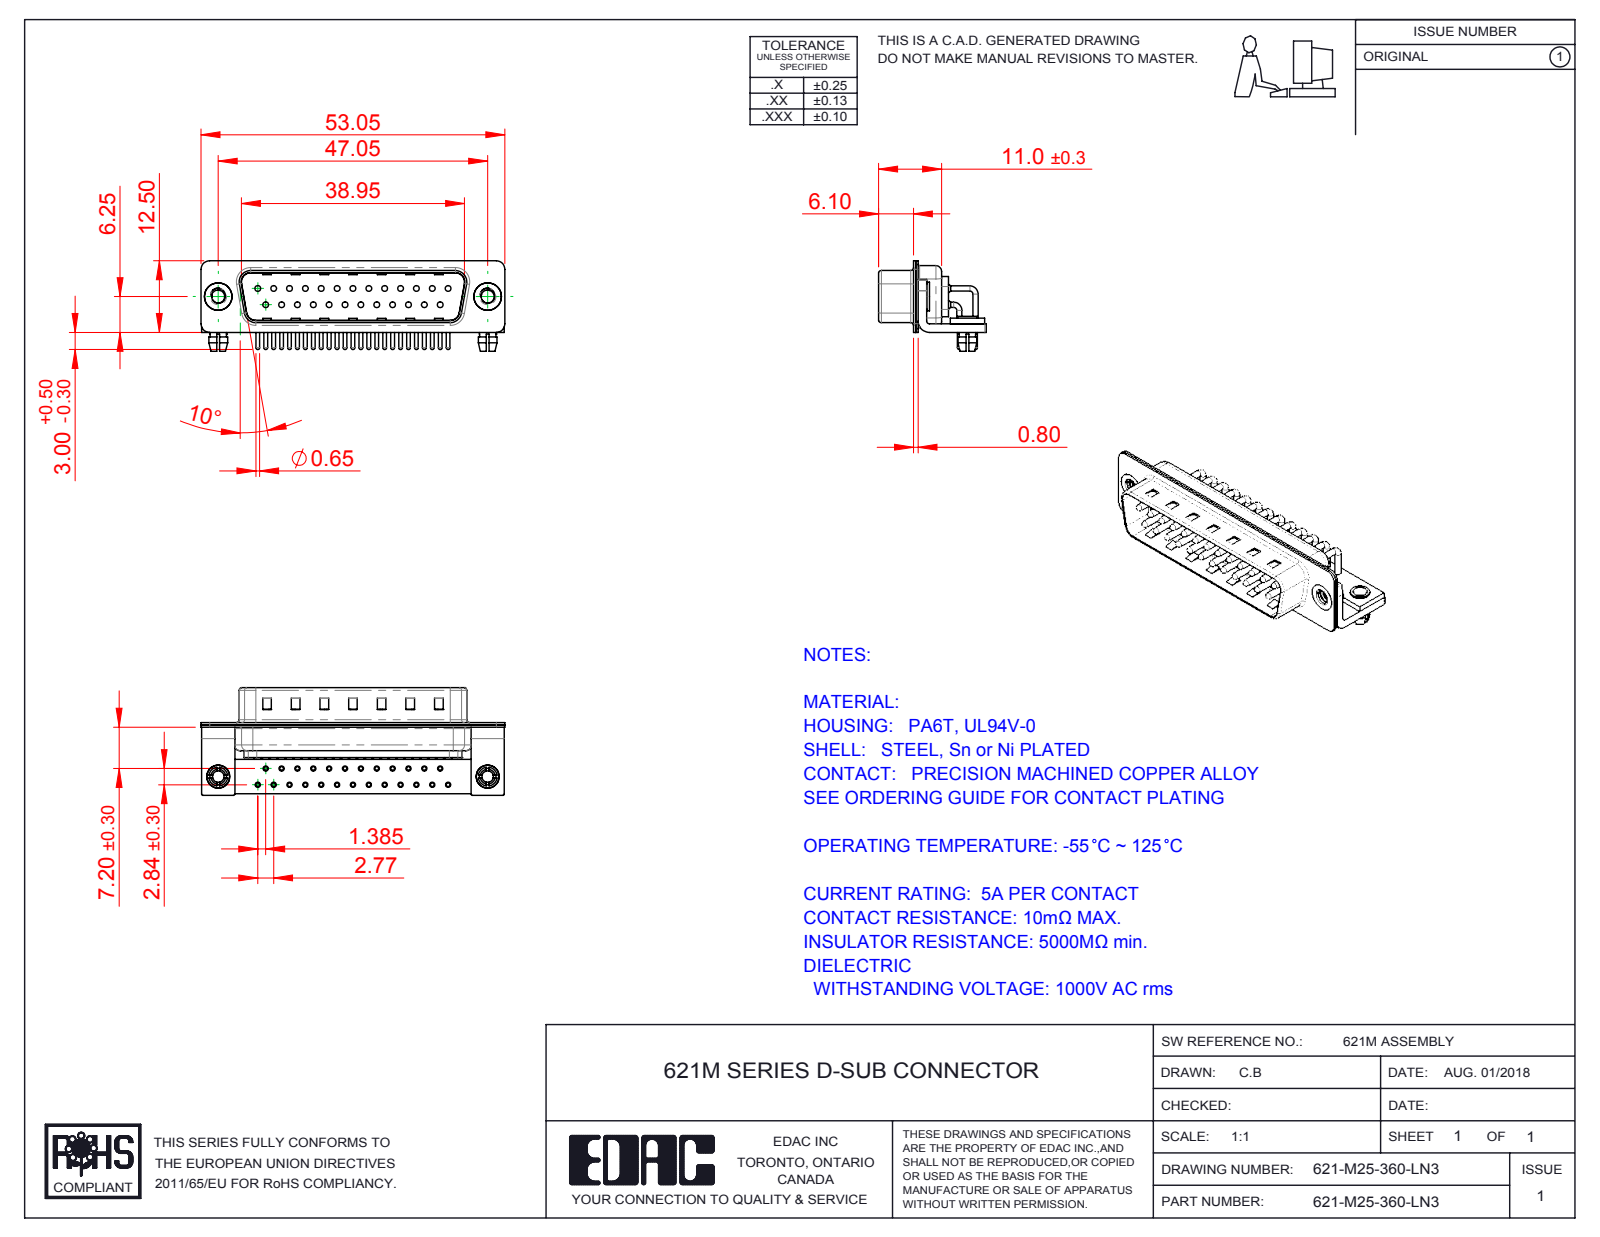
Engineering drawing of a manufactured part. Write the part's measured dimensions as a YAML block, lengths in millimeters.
part_name: "621M Board Lock; 621M Stabilizer Bracket; 621M Contact Row 2; 621-M25-360-LN3 (+6 more)"
step_written_by: "SolidWorks 2016 (CONFIG_CONTROL_DESIGN)"
units: millimeters
bodies: {solids: 35, faces: 3318, planar: 1845, cylindrical: 1141, other: 332}
overall_size: [53.05, 18.8, 15.8]
volume: 3431
surface_area: 9130
round_holes:
  - {diameter: 2, count: 27}
  - {diameter: 0.9, count: 25}
  - {diameter: 1, count: 25}
  - {diameter: 1.7, count: 25}
  - {diameter: 2.26, count: 2}
  - {diameter: 2.5, count: 2}
  - {diameter: 3.2, count: 2}
  - {diameter: 4, count: 2}
  - {diameter: 4.8, count: 2}
round_bosses_or_shafts:
  - {diameter: 0.9, count: 33}
  - {diameter: 1.5, count: 25}
  - {diameter: 0.65, count: 25}
  - {diameter: 5, count: 2}
  - {diameter: 4.9, count: 2}
  - {diameter: 4, count: 2}
  - {diameter: 3.4, count: 2}
  - {diameter: 3.3, count: 2}
partial_cylinders:
  - {radius: 1.01, count: 25}
  - {radius: 0.25, count: 16}
  - {radius: 1.5, count: 16}
  - {radius: 2, count: 13}
  - {radius: 0.5, count: 9}
  - {radius: 1.6, count: 8}
  - {radius: 0.6, count: 4}
  - {radius: 0.65, count: 4}
face_to_face_distances: [0.4, 0.85, 1.25, 1.5, 9.55, 10.4, 0.8, 1, 8.3, 8.7]
hole_center_spacings: [3.16, 2.77, 8.31, 5.54, 11.08, 13.85, 5.04, 16.62]
